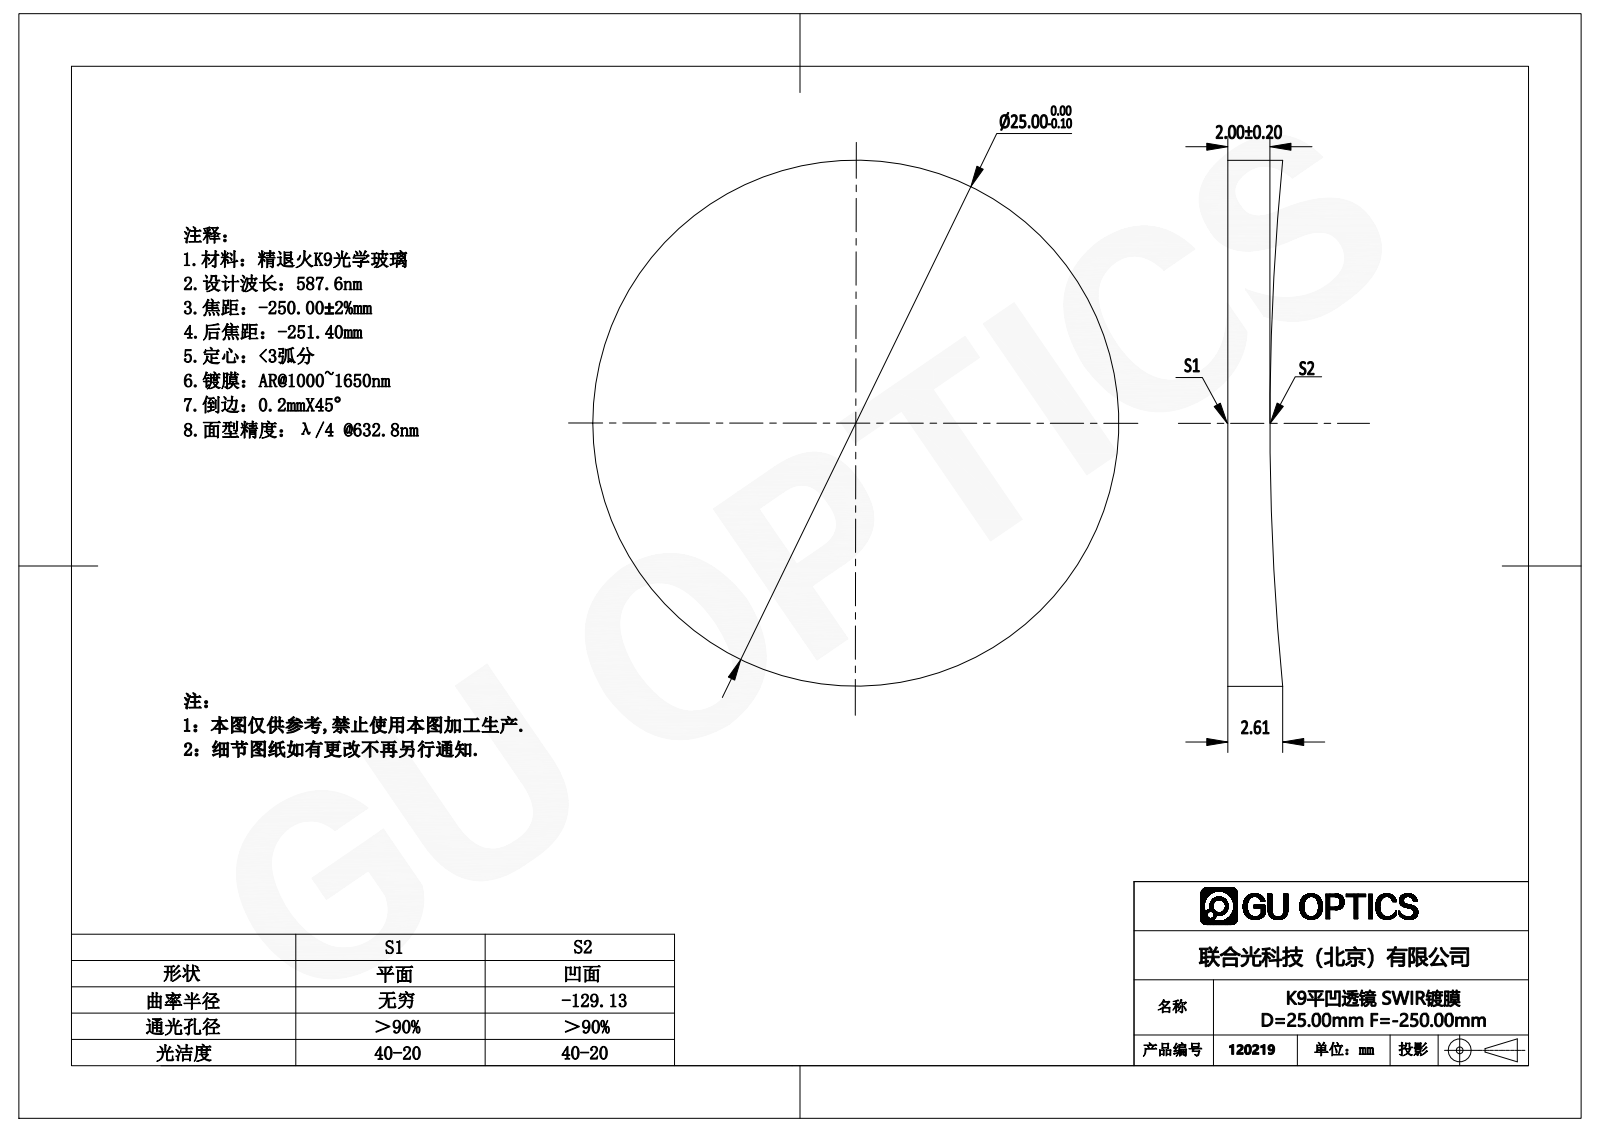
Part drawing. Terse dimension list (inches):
name: 120159
written by: SolidWorks 2016 (AUTOMOTIVE_DESIGN)
unit: in
bodies: 1 solid, 5 faces (1 planar, 2 cylindrical, 2 other)
size: 0.984 × 0.984 × 0.103
volume: 0.069 in³; area: 1.841 in²
bosses: 1× ⌀0.984
